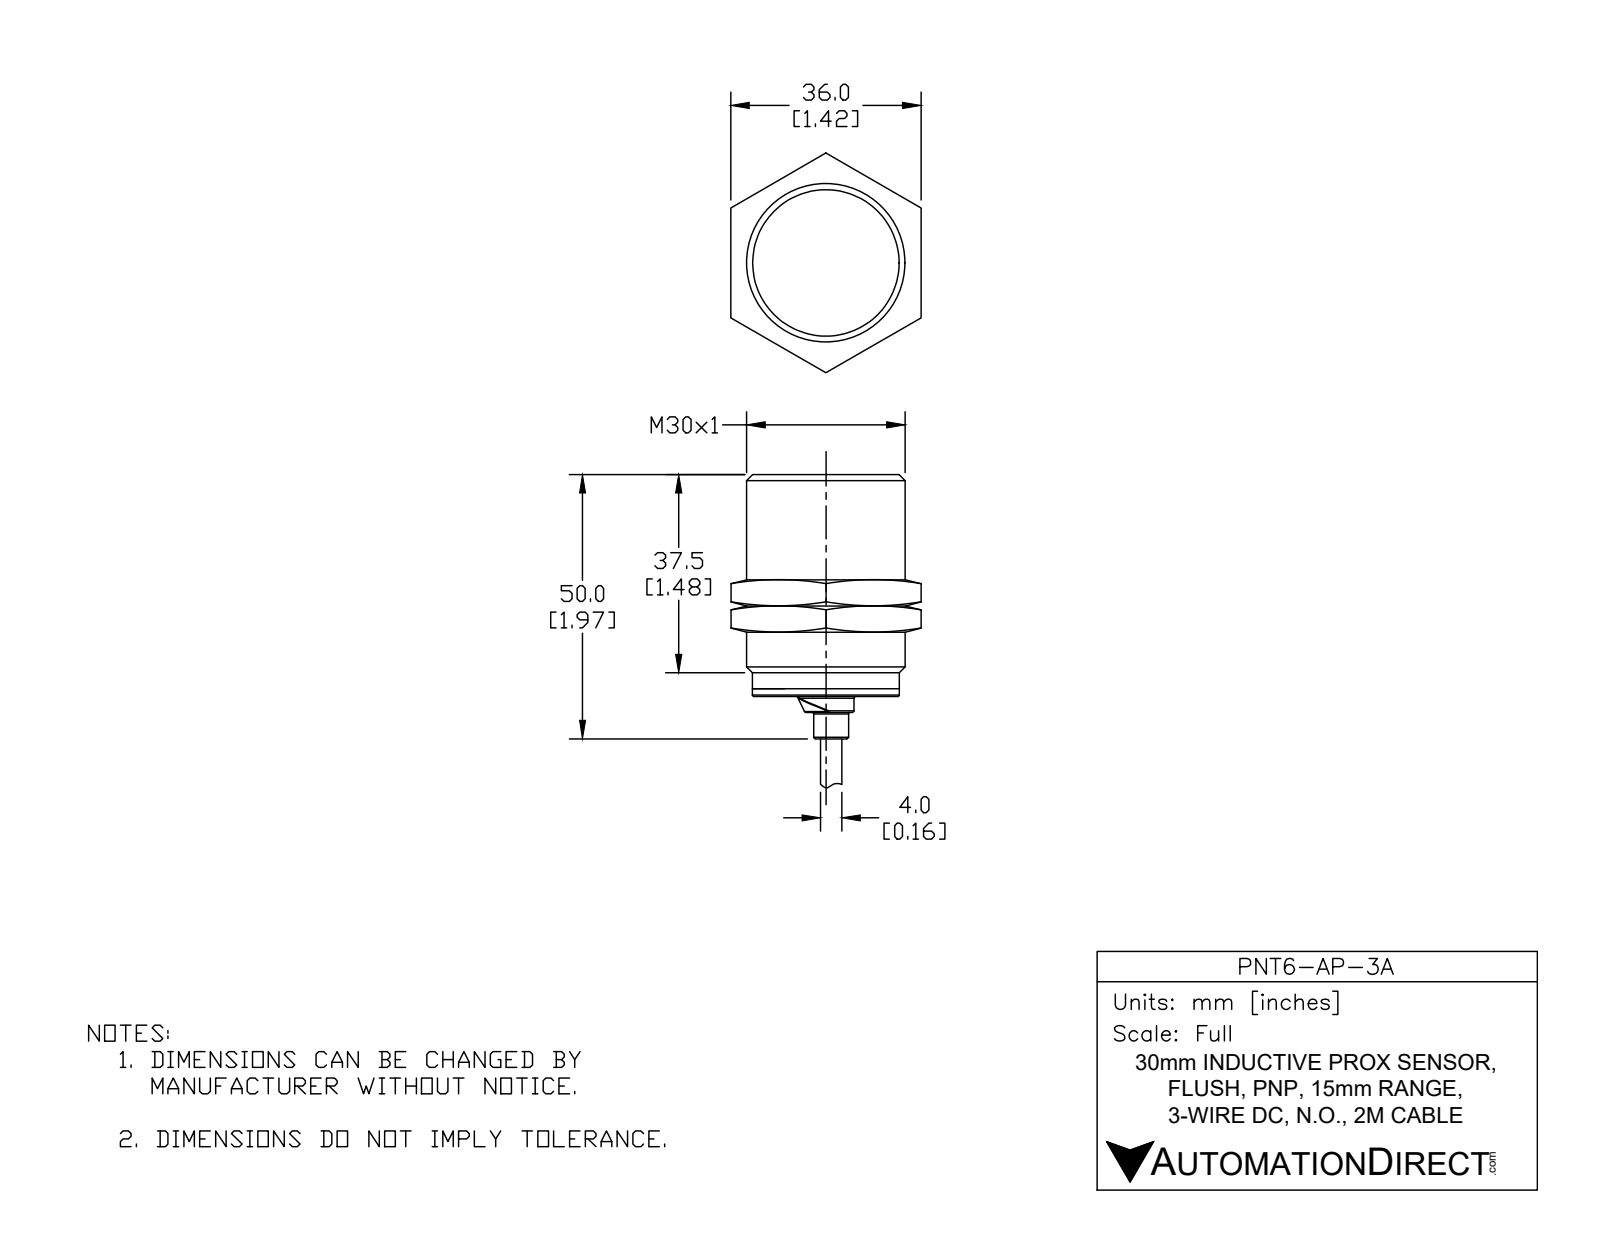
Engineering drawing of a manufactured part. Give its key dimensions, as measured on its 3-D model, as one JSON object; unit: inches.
{"part_name": "PNT6-AP-3A", "step_written_by": "SolidWorks 2017 (AUTOMOTIVE_DESIGN)", "units": "inches", "bodies": {"solids": 1, "faces": 77, "planar": 15, "cylindrical": 30, "other": 32}, "overall_size": [3.969, 1.181, 1.181], "volume_in3": 1.84, "surface_area_in2": 9.715, "round_holes": [[0.162, 1]], "round_bosses_or_shafts": [[0.049, 6], [1.181, 1], [1.095, 1], [1.094, 1], [0.417, 1], [0.26, 1], [0.157, 1]], "partial_cylinders_radius": [[0.077, 1]], "face_to_face_distances": [1.654, 1.772, 0.118, 1.969, 0.315, 0.197, 3.969, 2.315, 2.197, 2]}
